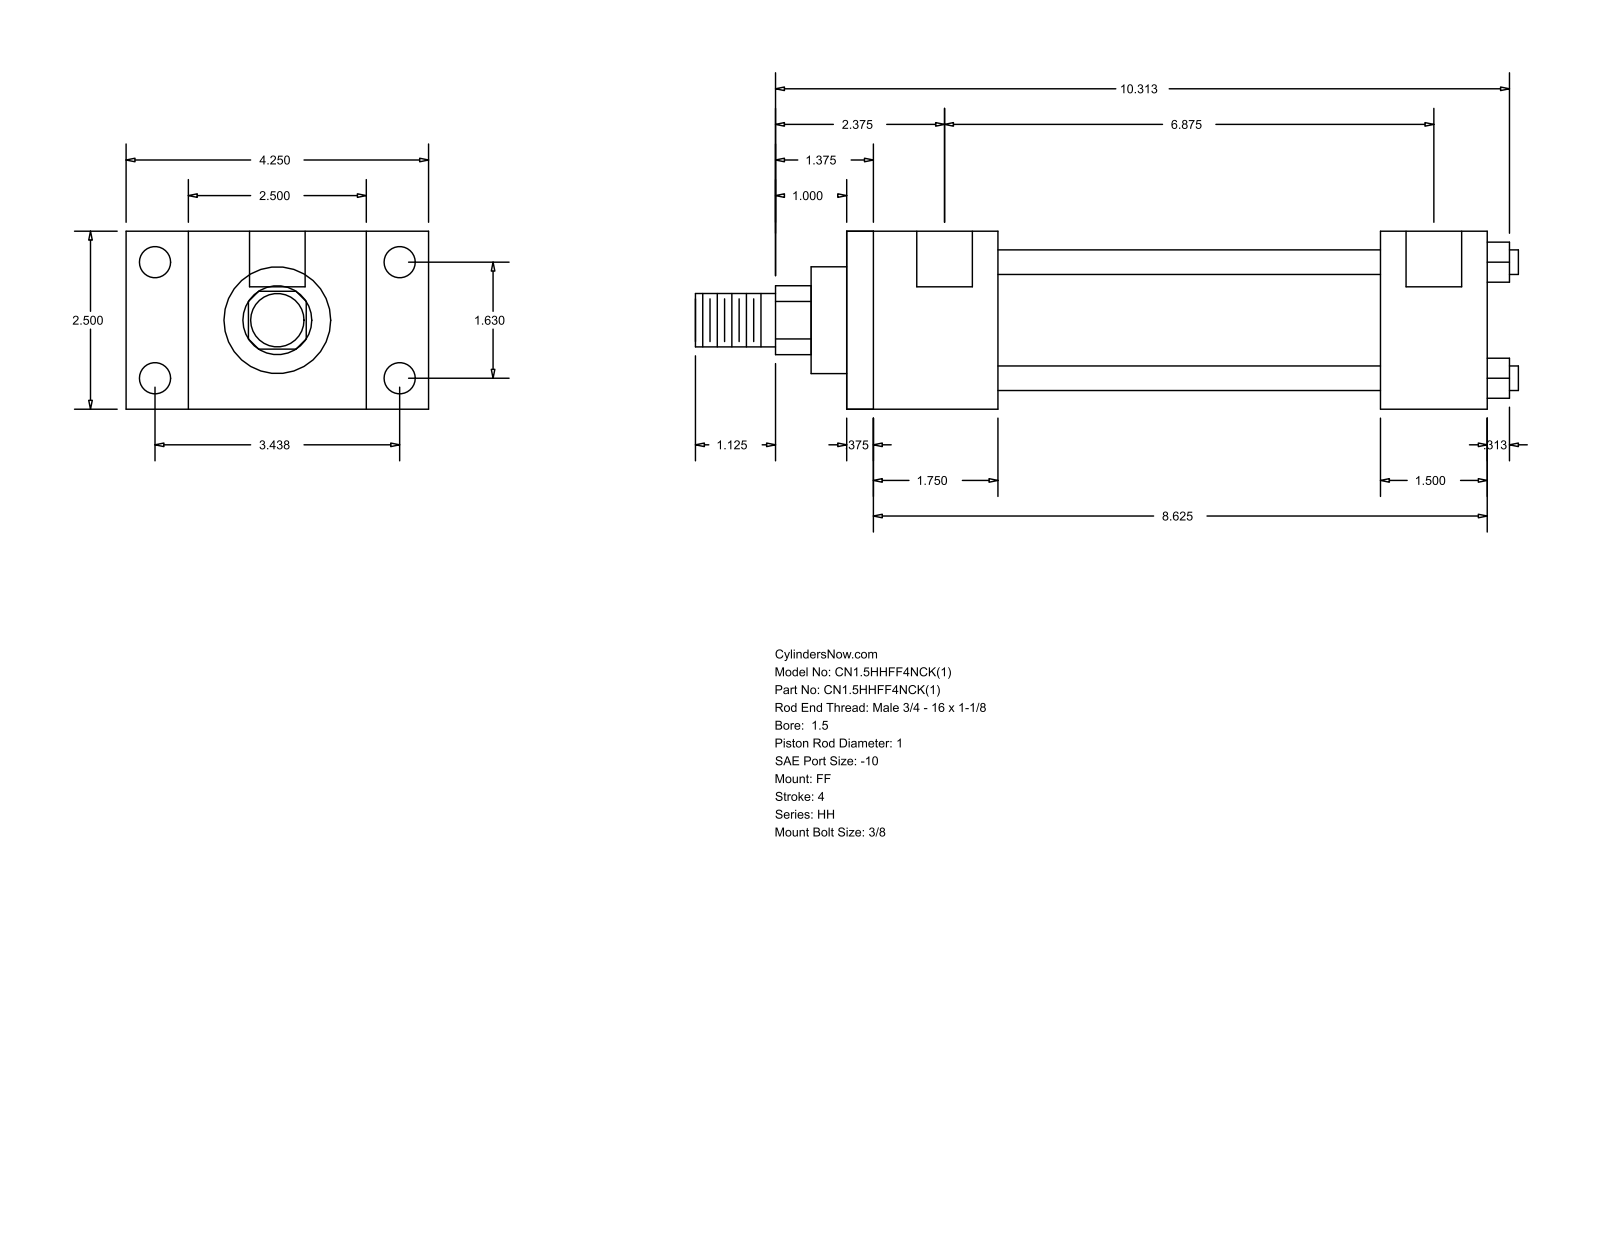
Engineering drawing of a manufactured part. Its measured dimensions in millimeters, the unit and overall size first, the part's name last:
Units: millimetres
Overall size (bounding box): 293.69 × 107.95 × 63.5
Round holes (diameter × count): ⌀5.56 ×4, ⌀11.13 ×4, ⌀19.84 ×2
Round bosses / shafts (diameter × count): ⌀8.76 ×4, ⌀44.45 ×1, ⌀38.1 ×1, ⌀25.4 ×1, ⌀19.05 ×1
Partial cylindrical surfaces — rounded edges, fillets, slot ends (radius × count): R12.29 ×1
Main face-to-face distances: 63.5, 228.6, 9.52, 219.08, 38.1, 53.98, 44.46, 174.62, 190.5, 180.98
Hole centre spacings: 1.59, 41.4, 87.32, 96.64, 176.21, 177.8, 174.62
Bodies: 0 solids, 92 faces (64 planar, 28 cylindrical, 0 other)
Part name (STEP PRODUCT): HH_FF__0150_1
STEP written by: GSSL Pune (CONFIG_CONTROL_DESIGN)
